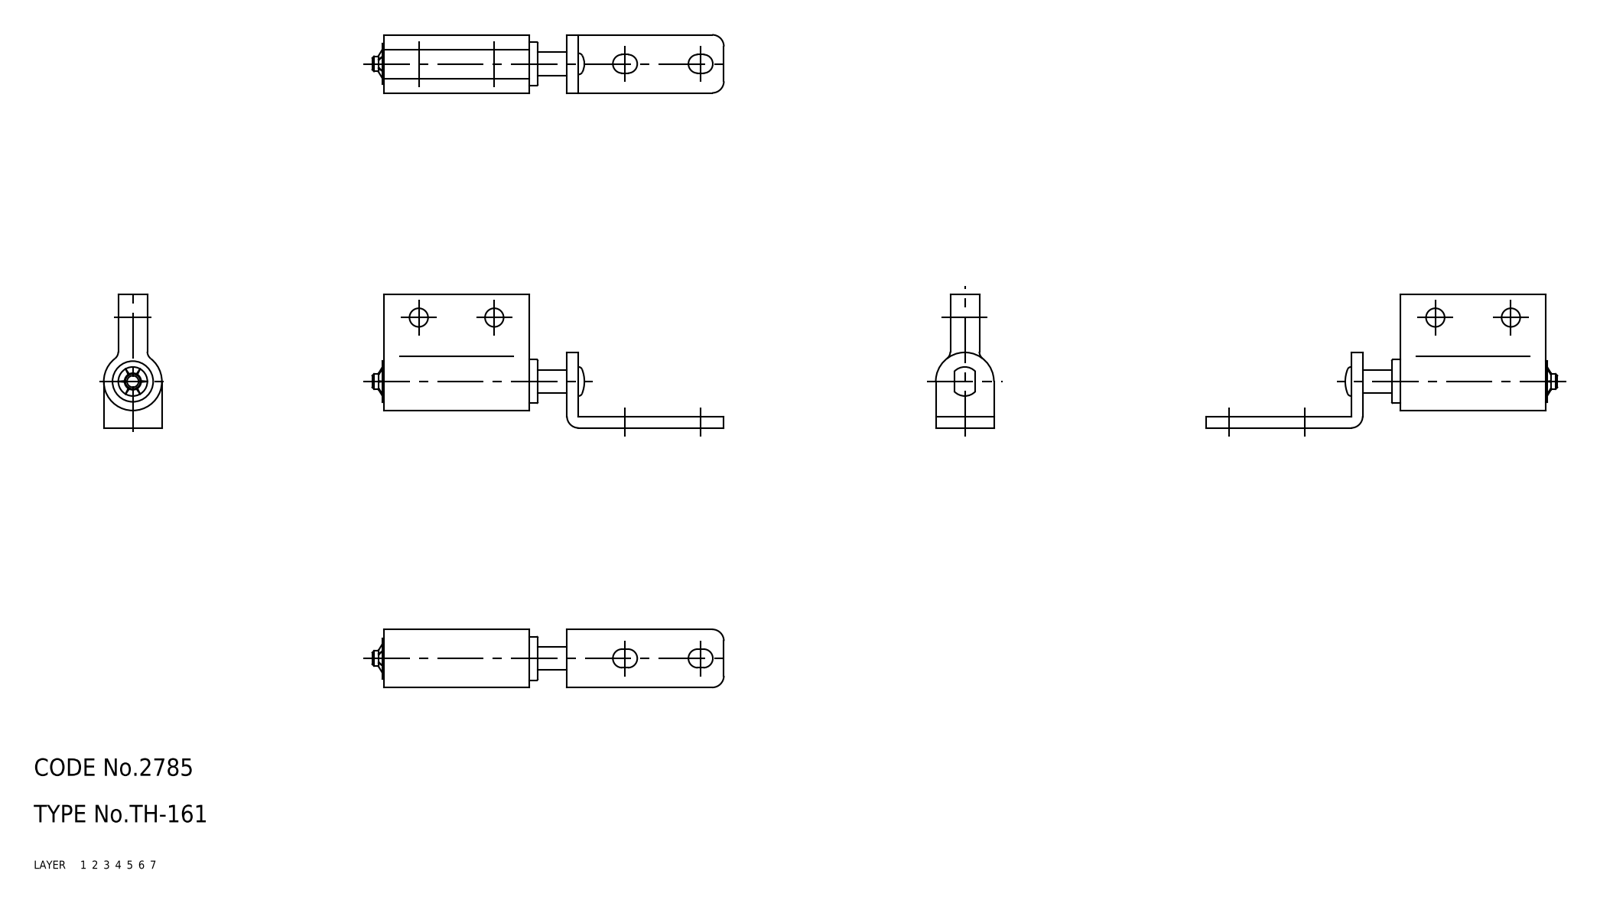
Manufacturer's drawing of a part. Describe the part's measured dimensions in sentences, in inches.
The part is named "67113842; 67113855; 67113868". Its 3-D file was written by "CADfix (AUTOMOTIVE_DESIGN)". It is 3 solids with 96 faces: 0 planar, 0 cylindrical and 96 other. Overall it measures 2.382 by 0.906 by 0.394 inches. Its volume is 0.245 cubic inches and its surface area 4.317 square inches.
